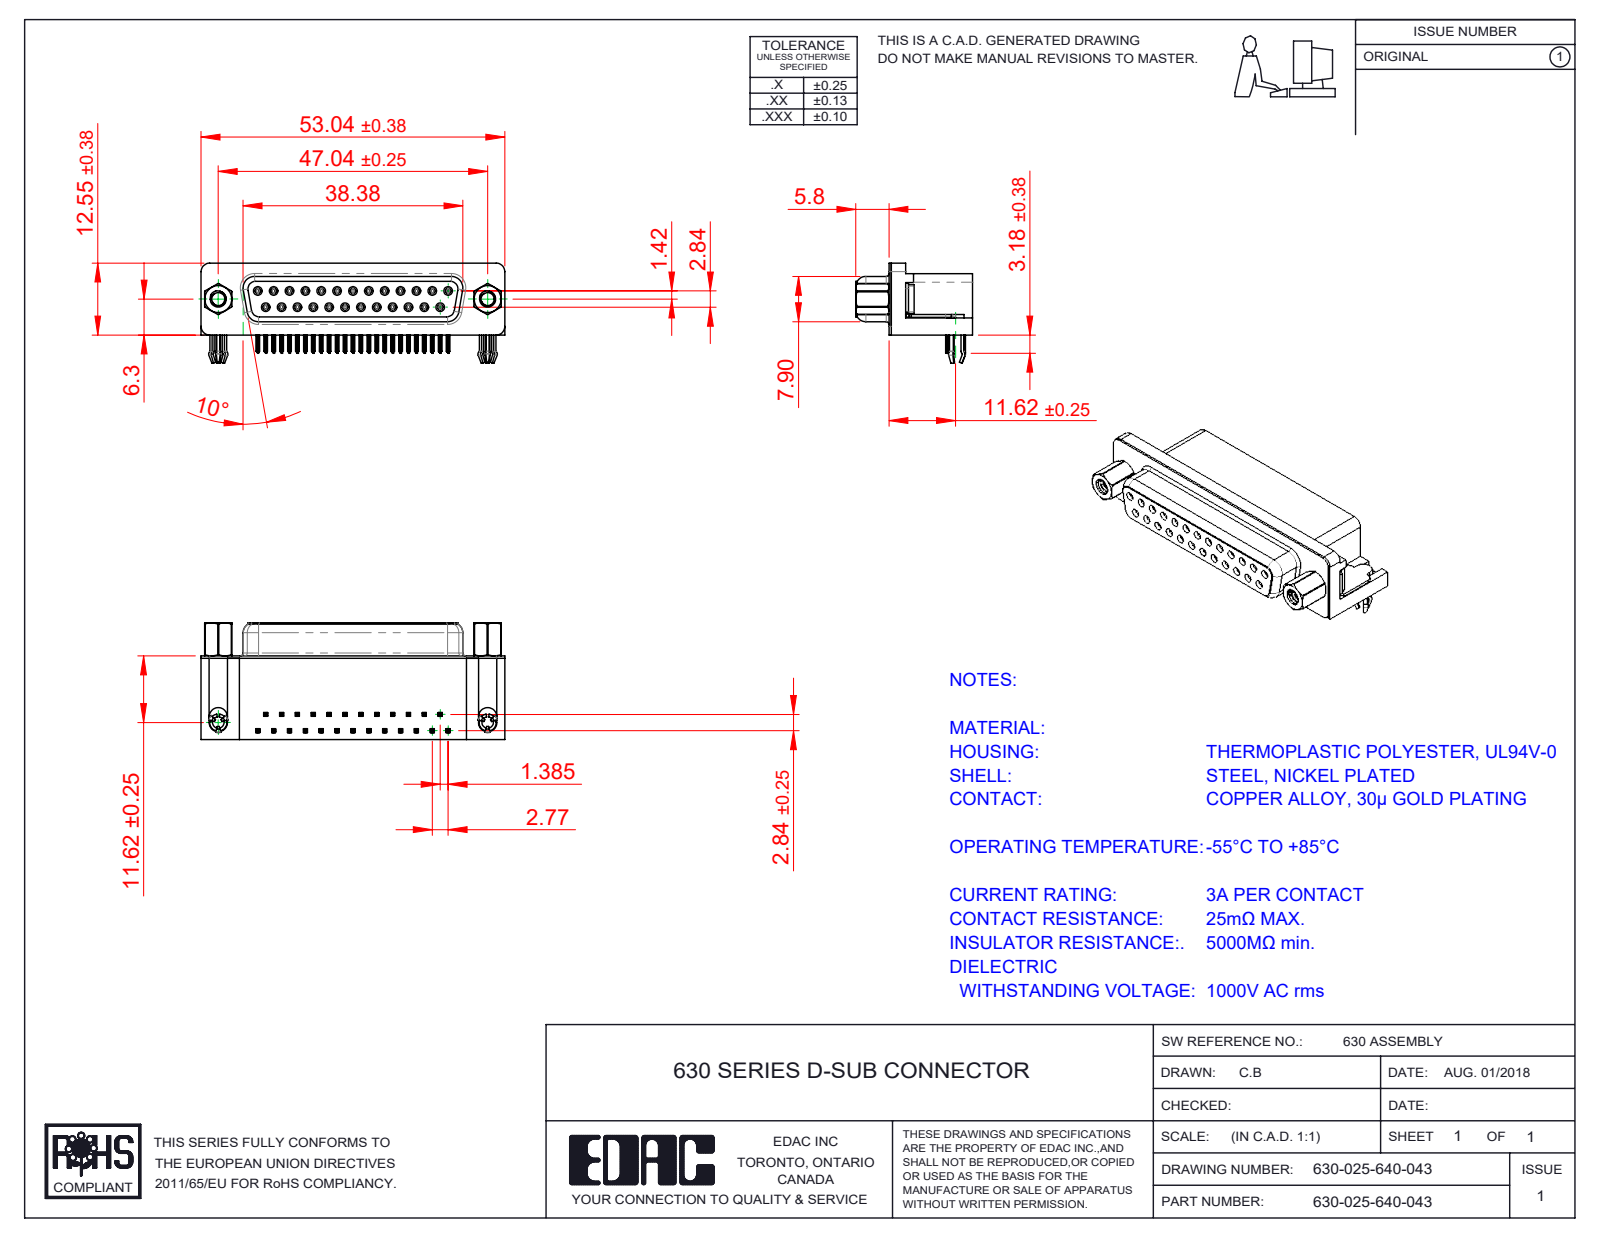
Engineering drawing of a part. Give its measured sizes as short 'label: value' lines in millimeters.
name: 630 4-40 Threaded Rivet; 630 Contact Bottom; 630 Contact Top; 630 Shell_25 Socket (+4 more)
written by: SolidWorks 2020 (CONFIG_CONTROL_DESIGN)
unit: mm
bodies: 33 solids, 4080 faces (1782 planar, 998 cylindrical, 1300 other)
size: 53.04 × 20.4 × 17.48
volume: 8 814 mm³; area: 10 649 mm²
holes: 25× ⌀0.8, 25× ⌀0.9, 2× ⌀2, 2× ⌀2.26, 2× ⌀2.29, 2× ⌀4, 2× ⌀4.8, 2× ⌀5
bosses: 25× ⌀1.2, 2× ⌀4.9, 2× ⌀4.75, 2× ⌀3.9, 2× ⌀3, 2× ⌀2.79
rounds: 200× R0.1, 100× R0.15, 50× R0.35, 25× R0.34, 18× R1, 12× R0.25, 12× R0.28, 8× R1.35
face distances: 0.4, 6.2, 10.35, 14.2, 2.73, 14.6, 0.85, 6.65, 2.84, 5.8
hole spacings: 3.16, 2.77, 5.54, 8.31, 11.08, 5.03, 5.04, 7.48
